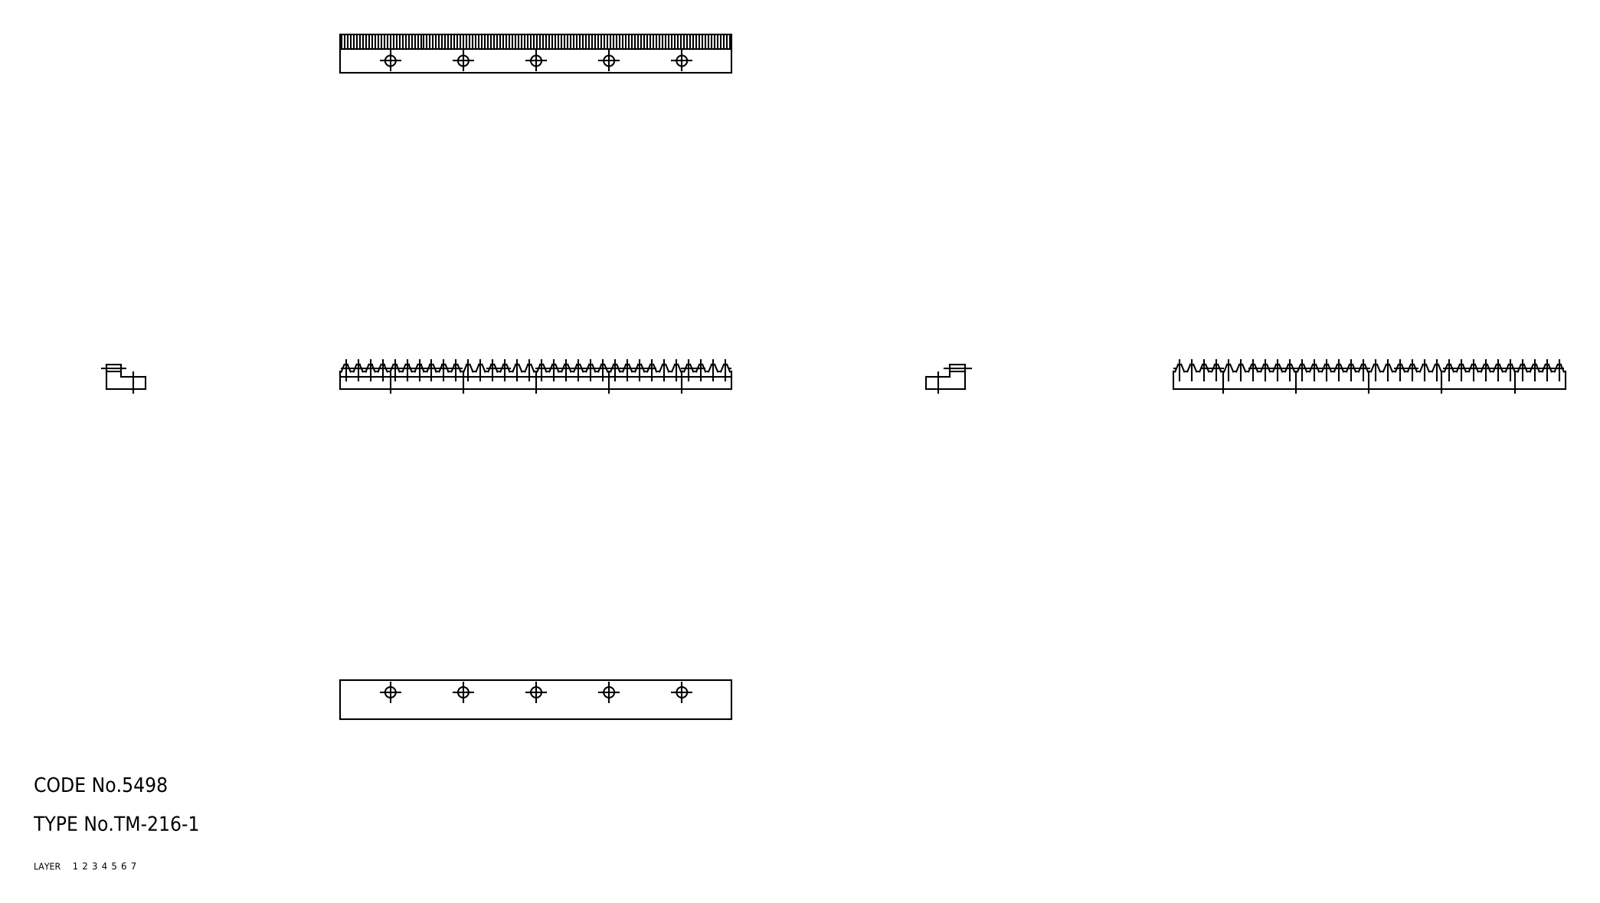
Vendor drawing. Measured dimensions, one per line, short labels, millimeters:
name: rack
written by: CADfix (AUTOMOTIVE_DESIGN)
unit: mm
bodies: 1 solid, 146 faces (0 planar, 0 cylindrical, 146 other)
size: 80.64 × 8 × 5
volume: 1 989 mm³; area: 2 262 mm²
